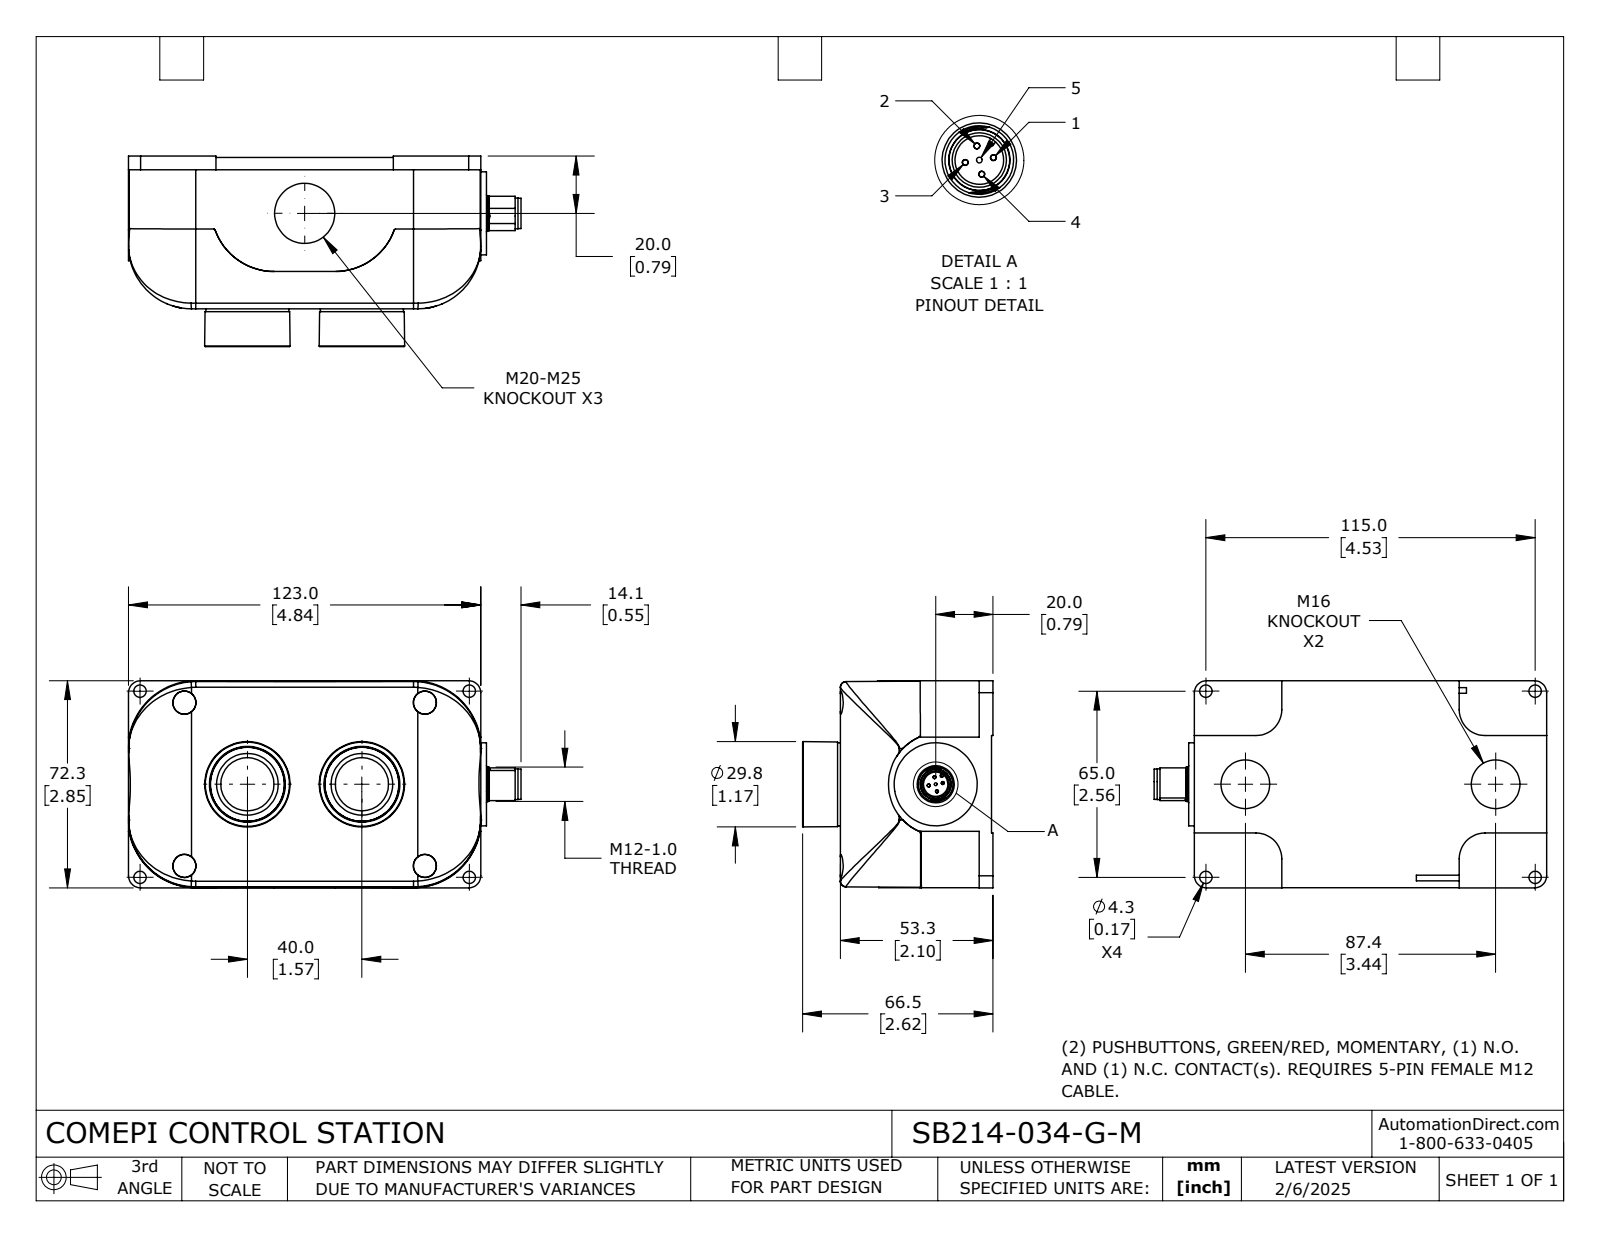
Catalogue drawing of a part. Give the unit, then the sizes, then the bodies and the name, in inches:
Units: inches
Overall size (bounding box): 5.396 × 2.846 × 2.618
Round holes (diameter × count): ⌀0.04 ×4, ⌀0.067 ×4, ⌀0.087 ×4, ⌀0.169 ×4, ⌀0.531 ×2, ⌀0.669 ×2, ⌀0.827 ×2, ⌀0.854 ×2, ⌀0.335 ×1
Round bosses / shafts (diameter × count): ⌀0.039 ×5, ⌀0.085 ×4, ⌀0.065 ×4, ⌀1.142 ×3, ⌀1.016 ×2, ⌀0.748 ×2, ⌀0.63 ×2, ⌀0.614 ×2
Partial cylindrical surfaces — rounded edges, fillets, slot ends (radius × count): R0.02 ×5, R0.01 ×4, R0.035 ×4, R0.079 ×4, R0.157 ×4, R0.354 ×4, R0.38 ×4, R0.866 ×4
Main face-to-face distances: 0.098, 2.079, 1.98, 0.118, 0.976, 0.878, 1.102, 2.098, 0.02, 2.618
Hole centre spacings: 1.39, 1.954, 3.309, 4.185, 0.098, 0.139, 0.139, 0.933
Volume: 16.54 in³ · Surface area: 129.7 in²
Bodies: 14 solids, 665 faces (255 planar, 235 cylindrical, 175 other)
Part name (STEP PRODUCT): SB214-034-G-M
STEP written by: SolidWorks 2024 (CONFIG_CONTROL_DESIGN)
